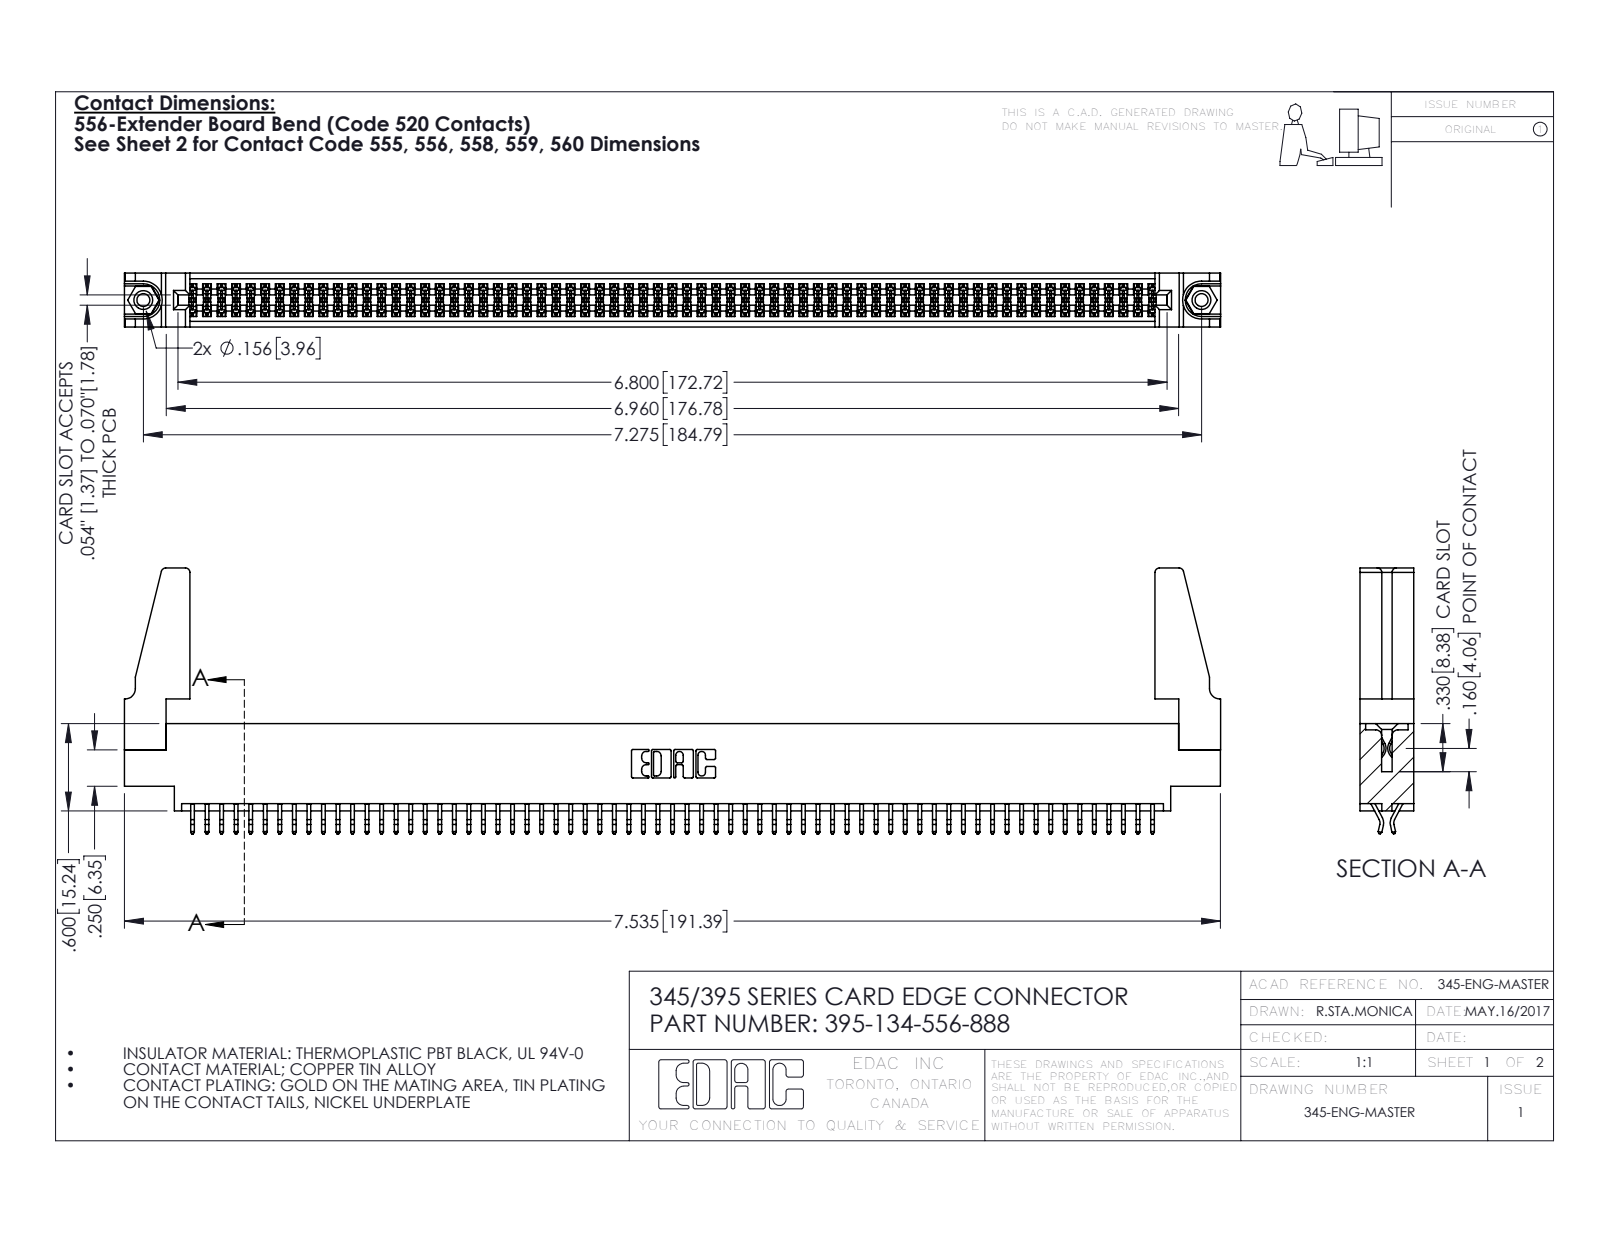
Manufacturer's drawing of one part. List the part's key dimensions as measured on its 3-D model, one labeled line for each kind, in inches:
Part name (STEP PRODUCT): 345-220-078_345-220-088; 345-250-001_345-250-001-102; 345 Part_0.170 Offset - 0.156 Dia-TH; 395-134-556-888 (+1 more)
STEP written by: SolidWorks 2016 (CONFIG_CONTROL_DESIGN)
Units: inches
Bodies: 139 solids, 7758 faces (5114 planar, 2628 cylindrical, 16 other)
Overall size (bounding box): 7.536 × 1.827 × 0.37
Volume: 1.34 in³ · Surface area: 48.49 in²
Round holes (diameter × count): ⌀0.089 ×2, ⌀0.125 ×2, ⌀0.156 ×2, ⌀0.064 ×1
Round bosses / shafts (diameter × count): ⌀0.155 ×2
Partial cylindrical surfaces — rounded edges, fillets, slot ends (radius × count): R0.006 ×201, R0.01 ×22, R0.03 ×8, R0.007 ×6, R0.031 ×6, R0.026 ×3, R0.01 ×2, R0.014 ×2
Main face-to-face distances: 0.072, 0.298, 0.37, 0.025, 0.098, 0.272, 0.2, 0.225, 0.175, 0.149
Hole centre spacings: 0.27, 7.039, 7.275
